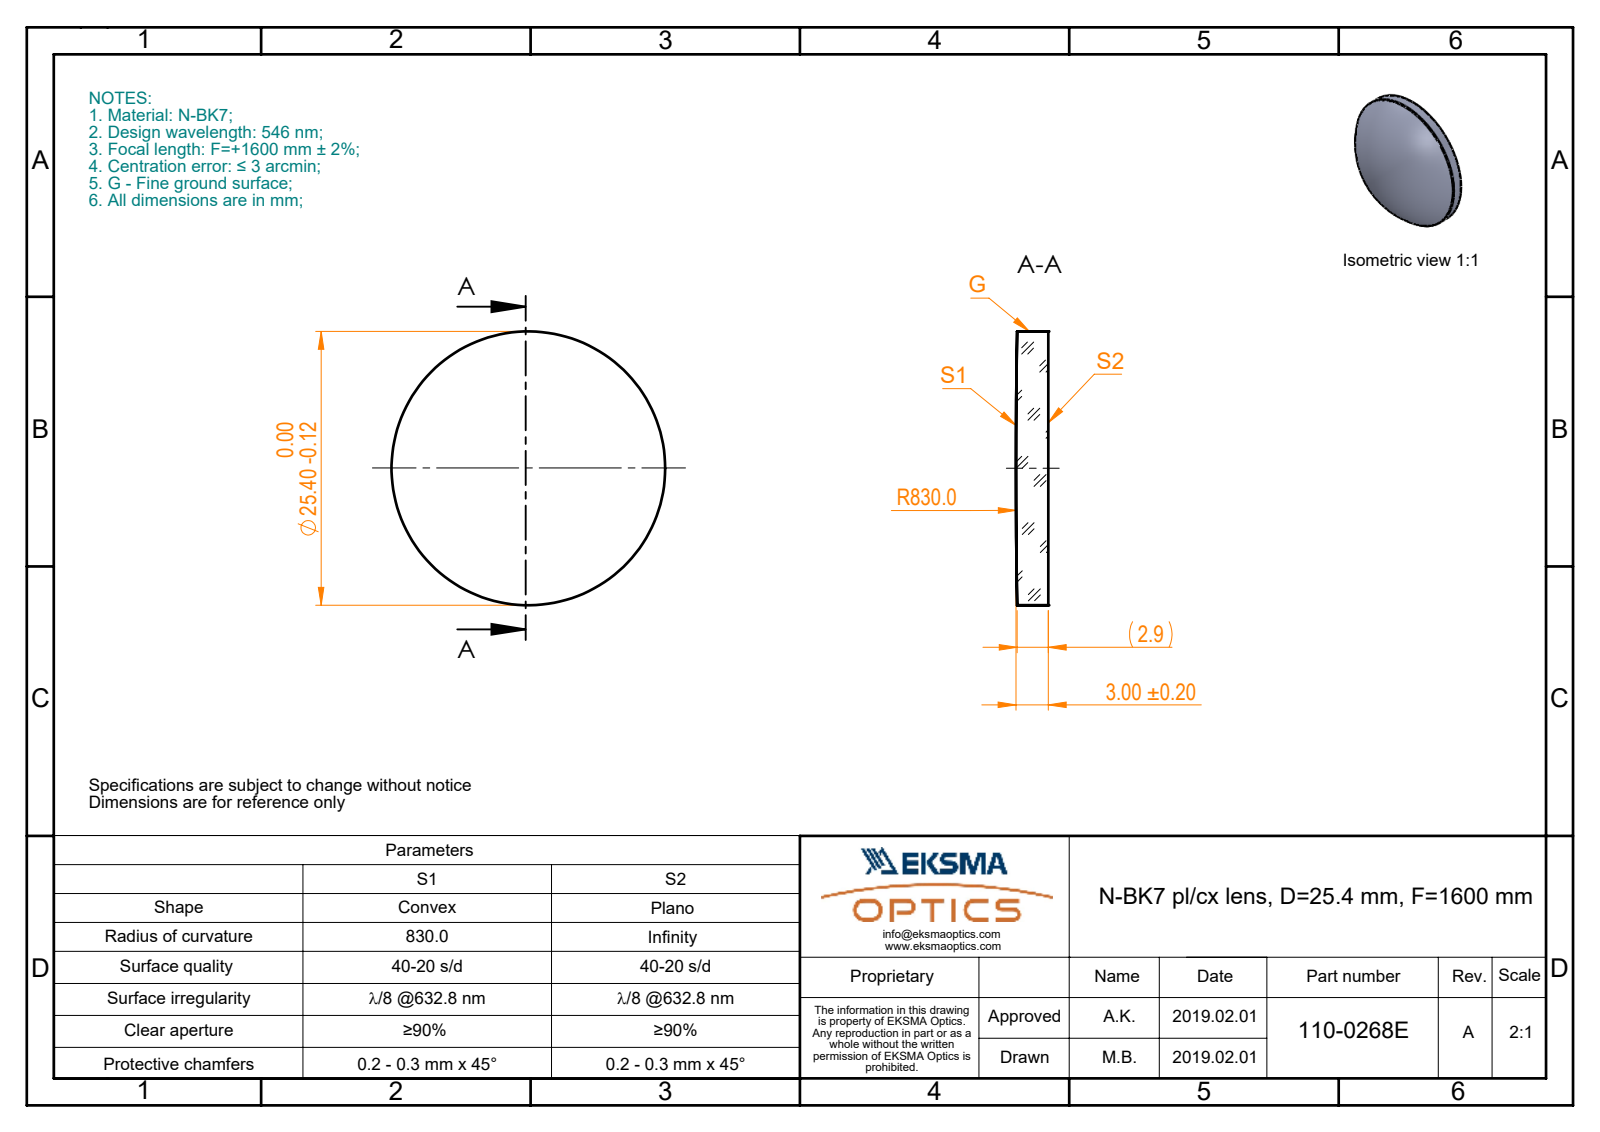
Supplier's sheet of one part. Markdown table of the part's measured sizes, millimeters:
| quantity | value |
| --- | --- |
| part name | 110-0268E BK7 pl-cx 25.4 F1600 |
| STEP written by | SolidWorks 2017 (CONFIG_CONTROL_DESIGN) |
| units | millimeters |
| bodies | 1 solid, 5 faces (1 planar, 2 cylindrical, 2 other) |
| overall size | 25.4 × 25.4 × 3 |
| volume | 1 496 mm³ |
| surface area | 1 245 mm² |
| round bosses / shafts (diameter × count) | 25.4 × 1 |
